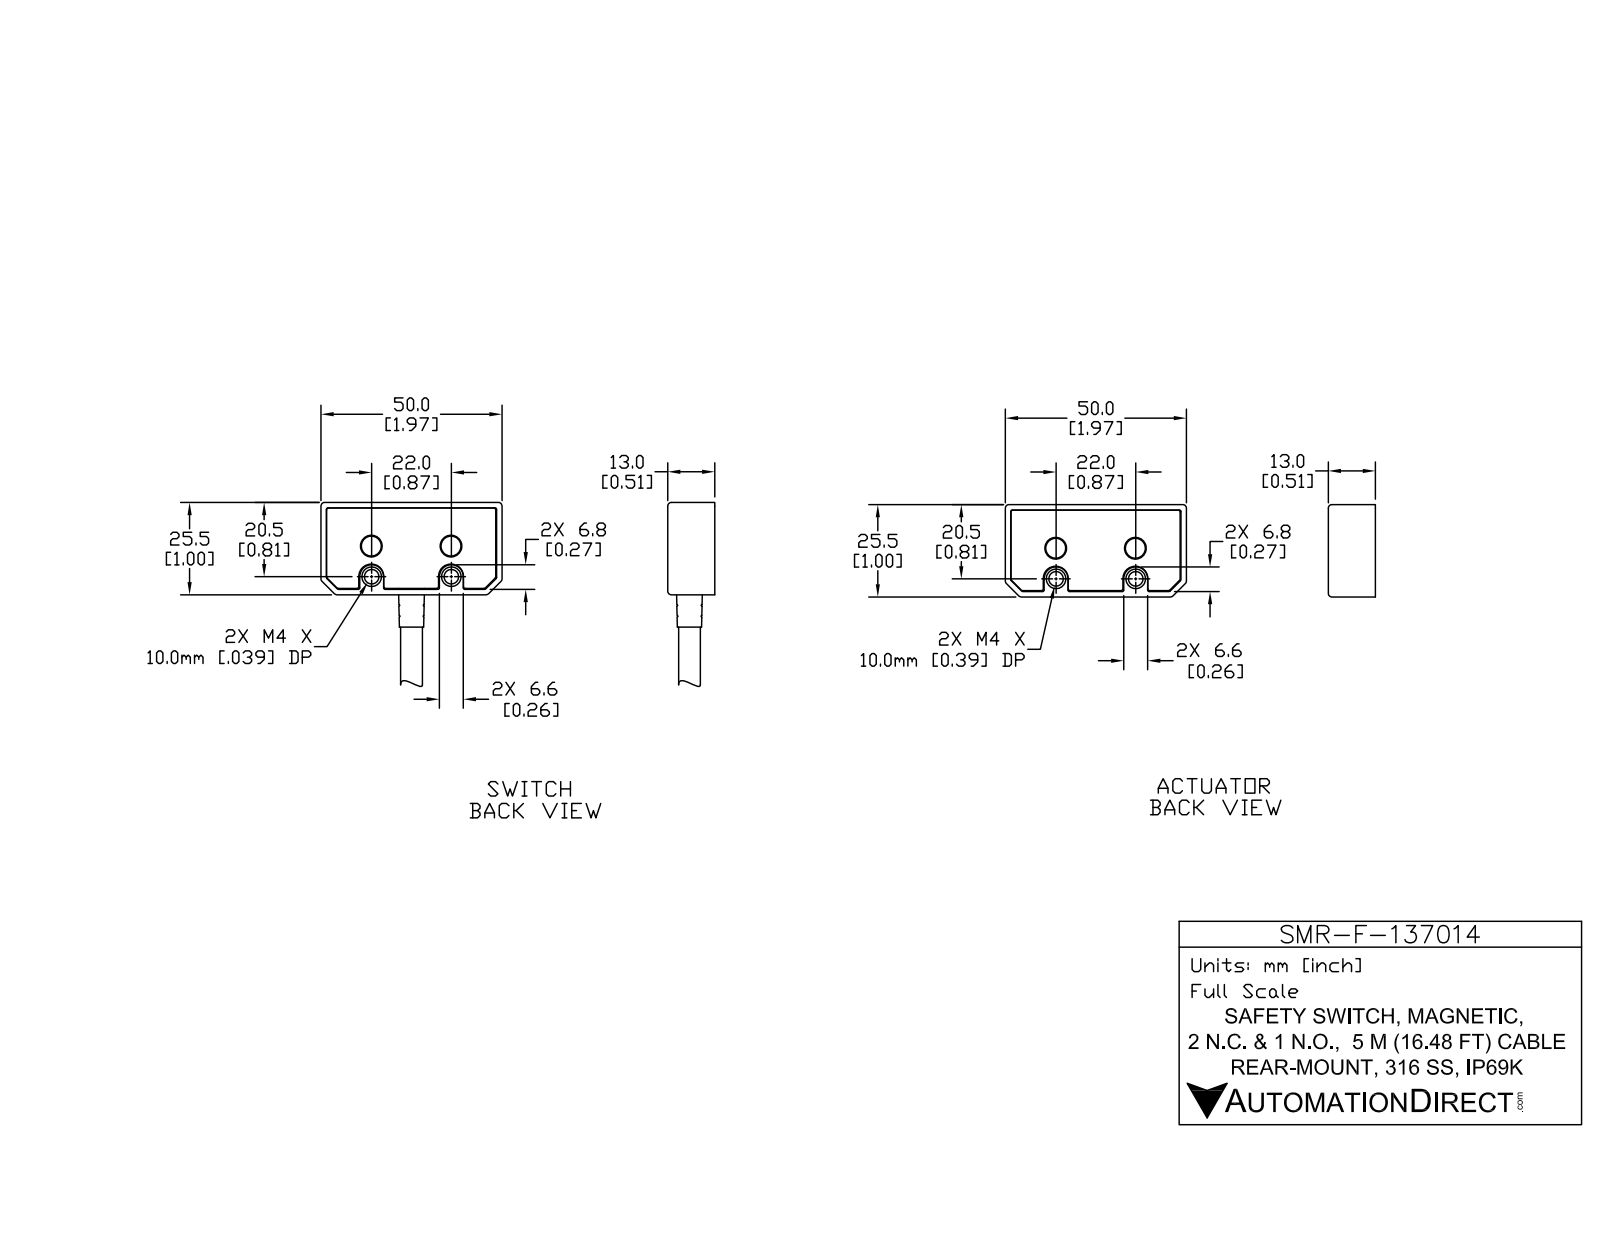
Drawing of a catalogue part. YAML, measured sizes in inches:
part_name: "SMR-F-137014_1; SMR-F-137014_2; SMR-F-137014"
step_written_by: "SolidWorks 2017 (AUTOMOTIVE_DESIGN)"
units: inches
bodies: {solids: 0, faces: 99, planar: 21, cylindrical: 36, other: 42}
overall_size: [6.063, 1.969, 0.551]
round_holes:
  - {diameter: 0.157, count: 2}
  - {diameter: 0.283, count: 1}
round_bosses_or_shafts:
  - {diameter: 0.157, count: 2}
  - {diameter: 0.236, count: 1}
partial_cylinders:
  - {radius: 0.039, count: 22}
face_to_face_distances: [0.551, 1.004, 1.043, 0.039, 1.969, 2.047, 2.617, 0.142, 0.862, 0.902]
hole_center_spacings: [0.866]
